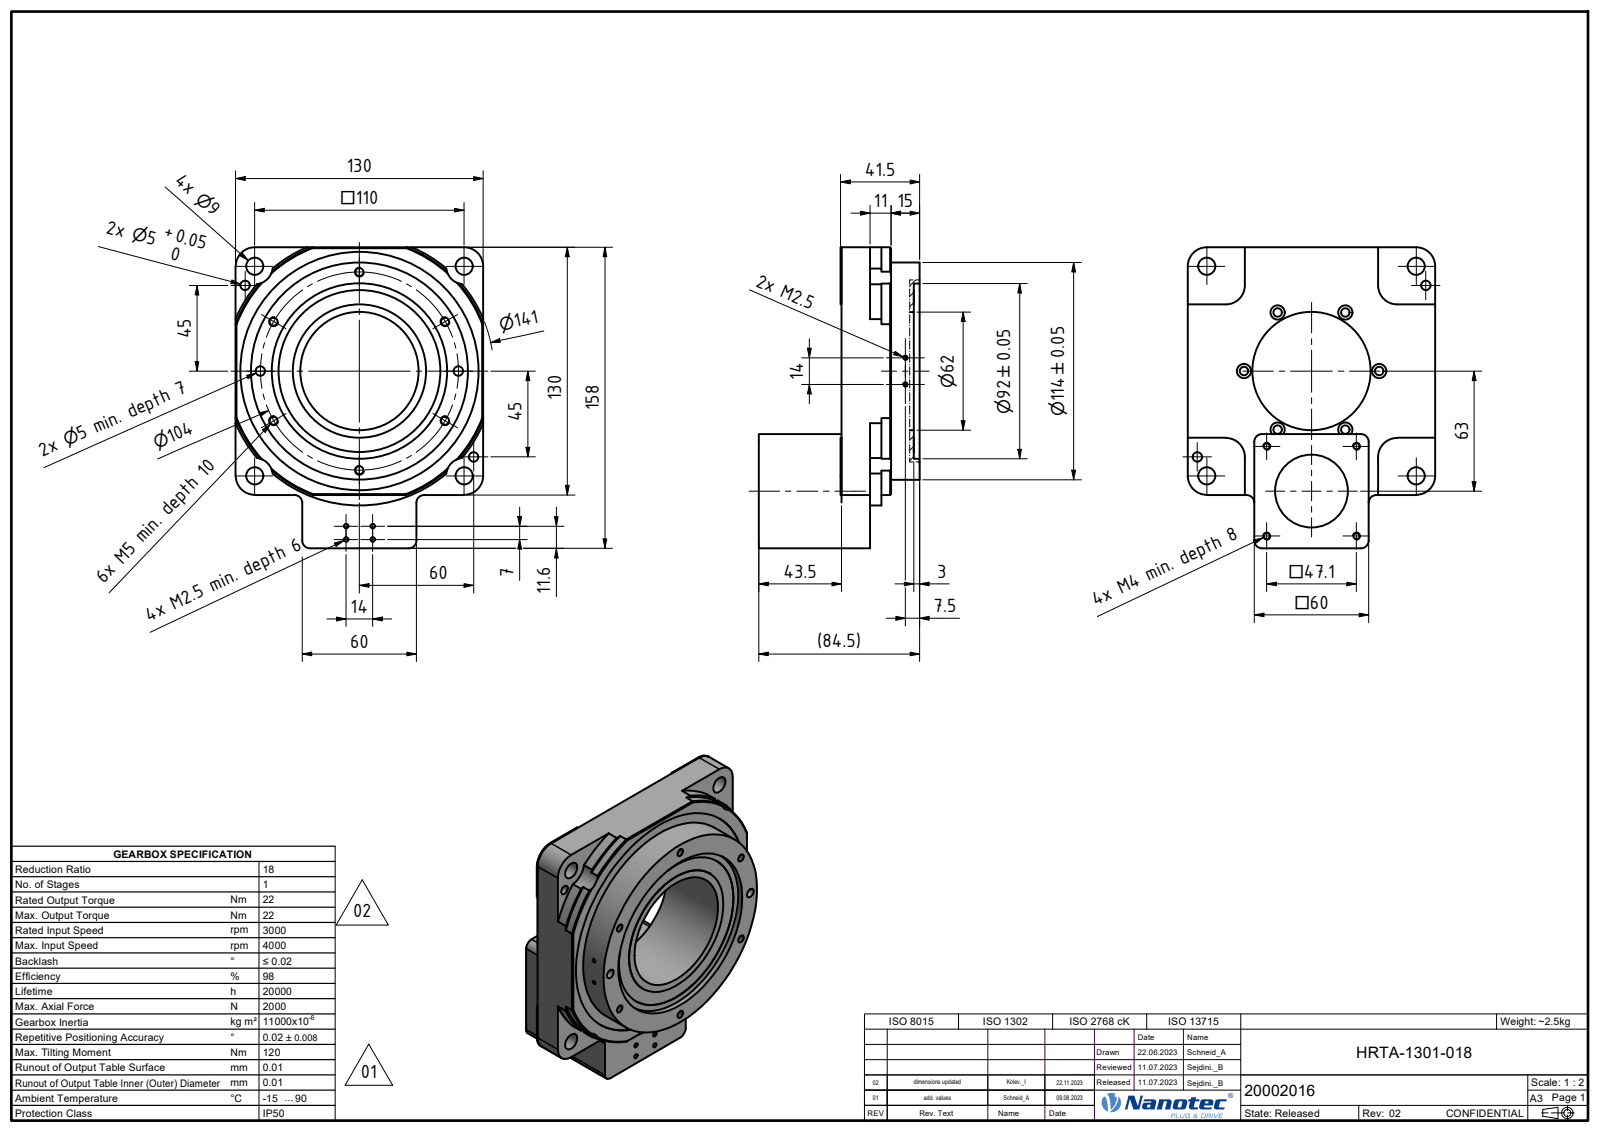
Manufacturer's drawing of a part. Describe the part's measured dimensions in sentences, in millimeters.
The part is named "上海固佐 ZTN130-18(6.35-38.1-47.14-47.14)". Its 3-D file was written by "Autodesk Inventor 2021 (AUTOMOTIVE_DESIGN)". It is 1 solid with 286 faces: 161 planar, 91 cylindrical and 34 other. Overall it measures 158 by 130 by 84.5 millimeters. Its volume is 596 469 cubic millimeters and its surface area 81 541 square millimeters. Round holes: 6 of diameter 2.05, 6 of diameter 4.2, 6 of diameter 7.5, 4 of diameter 3.3, 4 of diameter 5, 4 of diameter 8, 4 of diameter 9, 2 of diameter 9.1, 1 of diameter 30, 1 of diameter 38.1, 1 of diameter 44, 1 of diameter 62. Round bosses or shafts: 6 of diameter 7, 4 of diameter 7.6, 2 of diameter 9, 1 of diameter 114, 1 of diameter 70, 1 of diameter 39. Partial cylindrical surfaces (rounded edges, fillets, slot ends): 8 of radius 10, 6 of radius 4, 4 of radius 9.5, 1 of radius 69.5, 1 of radius 70.5. The main face-to-face distances are 26, 15, 35, 60, 12, 95, 38, 41, 41.5, 0.5. The hole center spacings are 35.5, 46.02, 76.22, 52, 13.31, 16.5, 26.99, 33.33.
